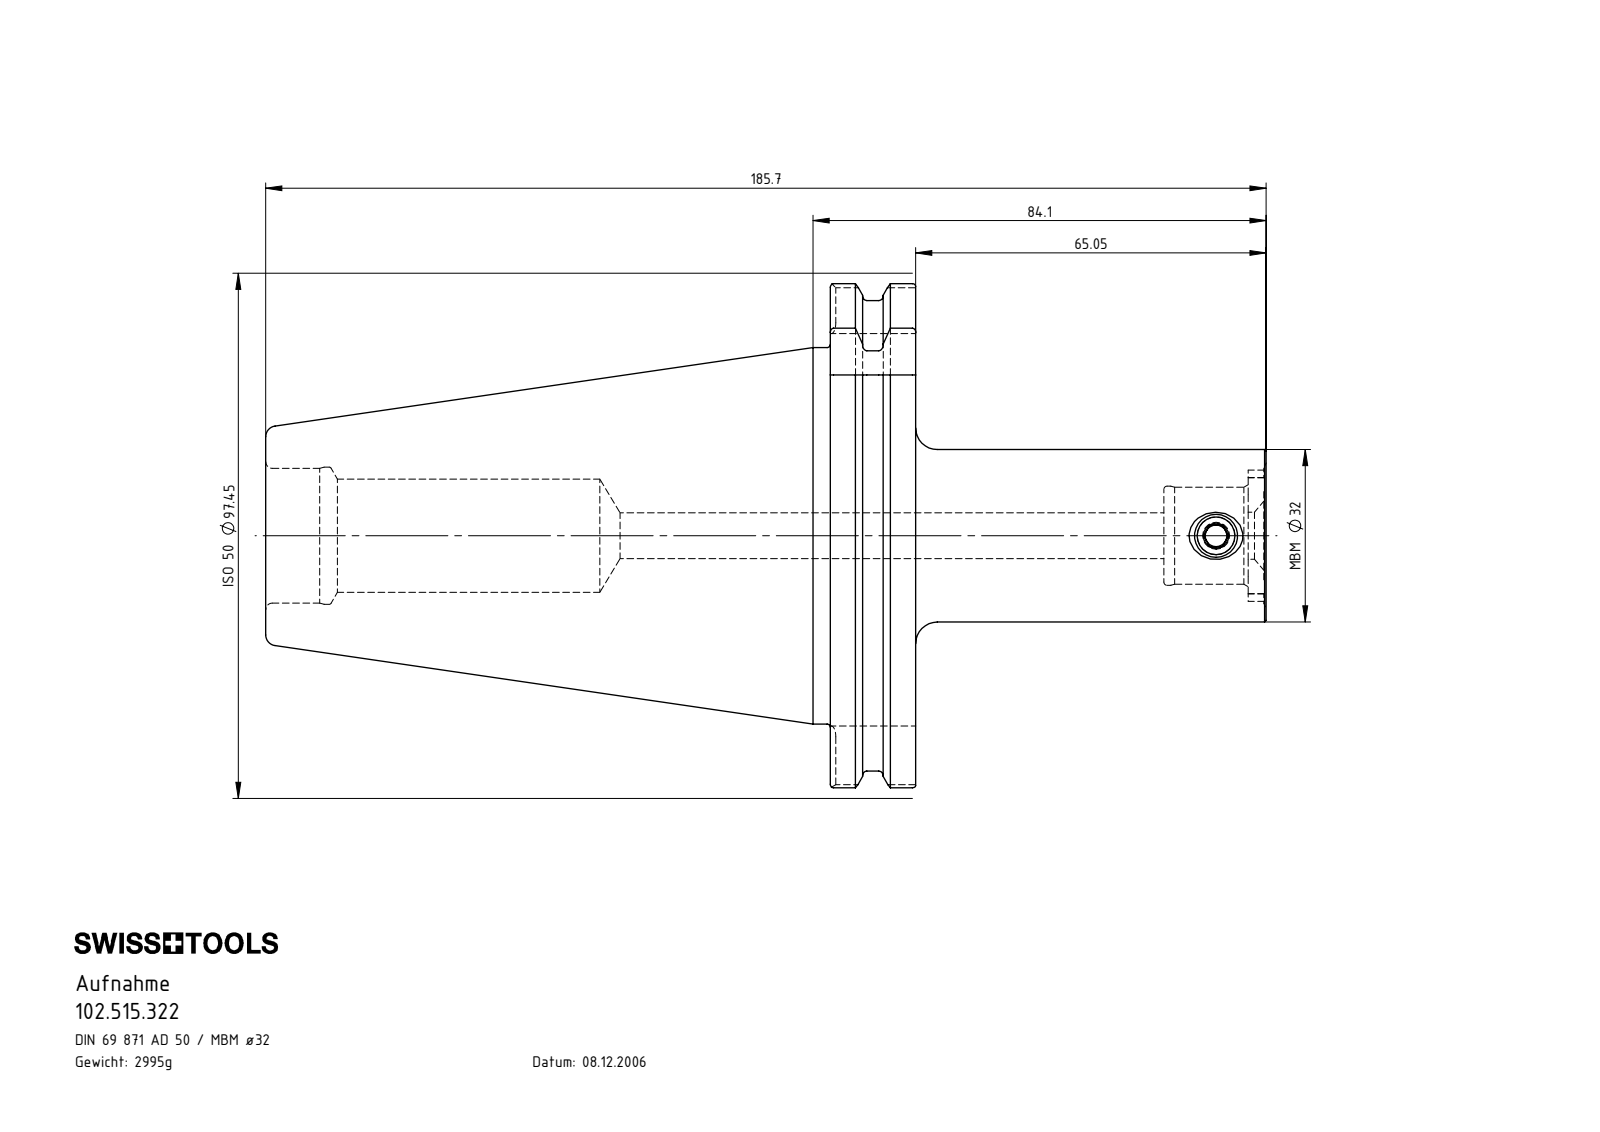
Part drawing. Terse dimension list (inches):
name: SK5-MB3.K01.084_C; MB3-ER1.001.011_A; 102.515.322
written by: SolidWorks 2017 (CONFIG_CONTROL_DESIGN)
unit: in
bodies: 2 solids, 171 faces (55 planar, 50 cylindrical, 66 other)
size: 7.311 × 3.837 × 3.681
volume: 23.29 in³; area: 77.73 in²
holes: 1× ⌀0.157, 1× ⌀0.276, 1× ⌀0.335, 1× ⌀0.709, 1× ⌀0.724, 1× ⌀0.827, 1× ⌀0.984, 1× ⌀1.002
bosses: 1× ⌀3.583, 1× ⌀2.75, 1× ⌀1.26, 1× ⌀0.315
rounds: 8× R0.079, 4× R0.126, 1× R0.48, 1× R1.919
face distances: 0.624, 4.126, 4.75, 2.866, 1.012, 7.311, 3.185, 2.561, 6.563, 2.437
